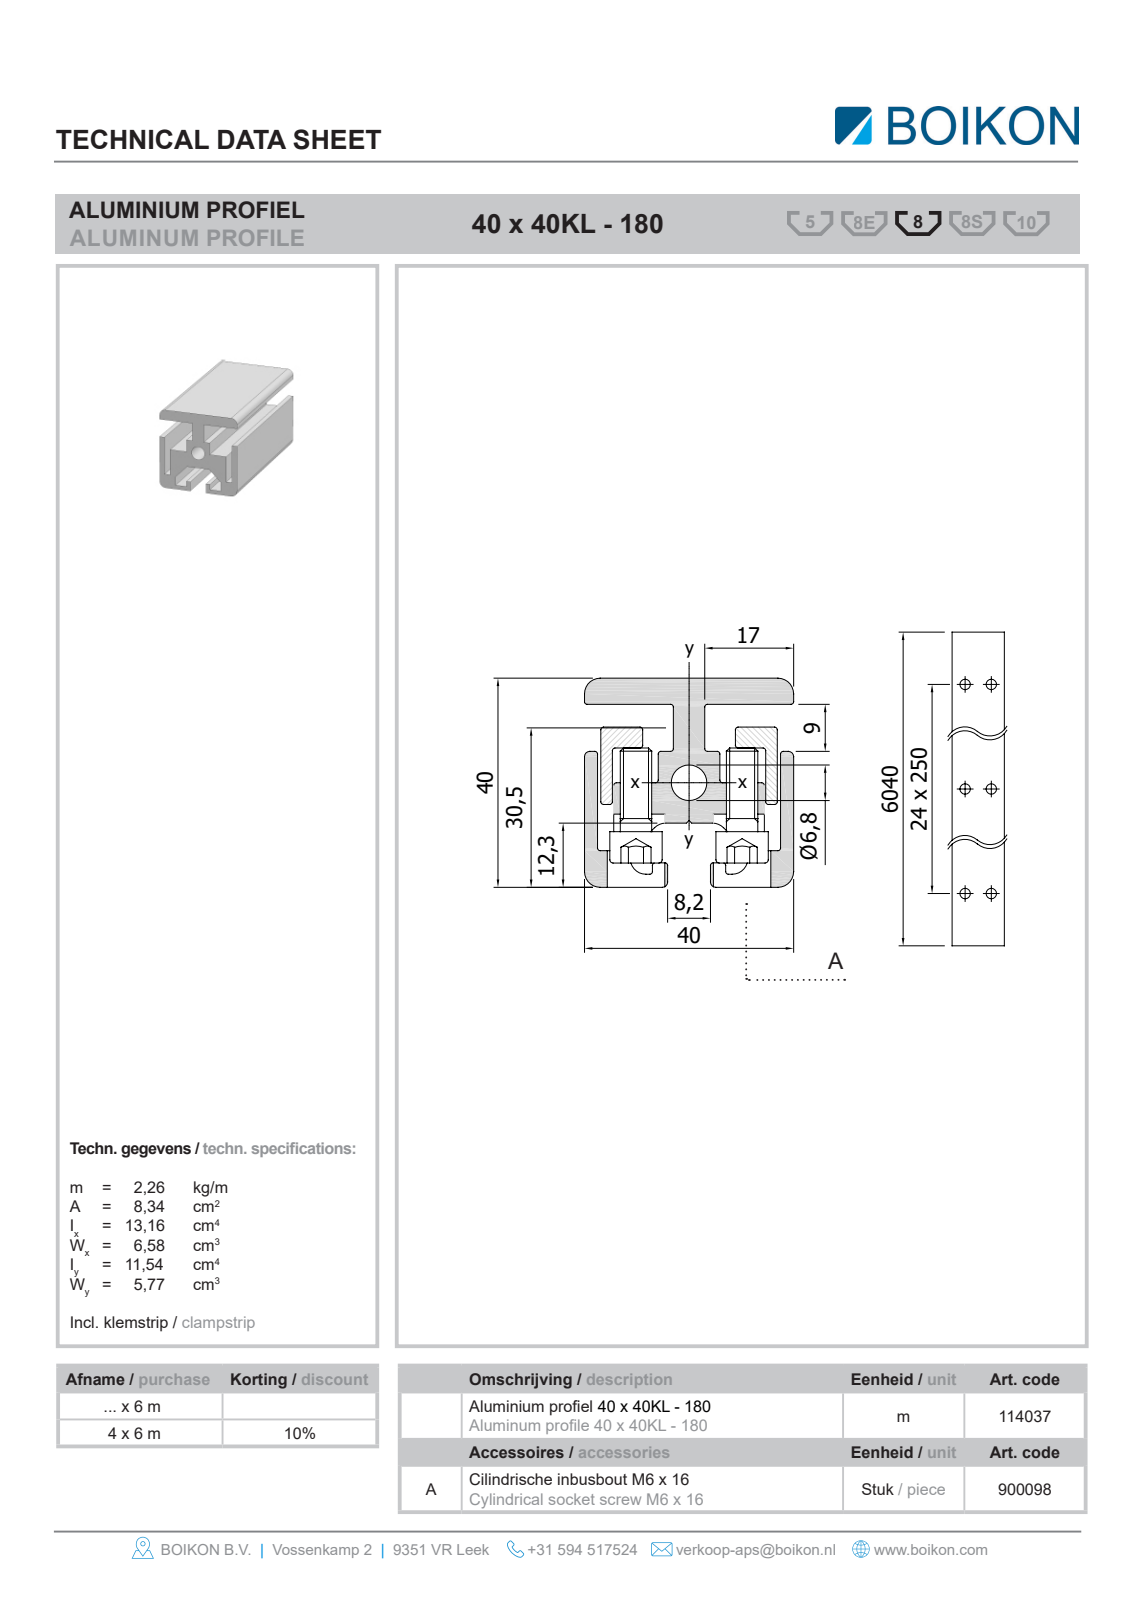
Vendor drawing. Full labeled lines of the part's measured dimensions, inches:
Part name (STEP PRODUCT): Root; 11403740x40-KL180BOIKON0
STEP written by: HiCAD 2013 1802.4 Build 509 (AUTOMOTIVE_DESIGN)
Units: inches
Bodies: 1 solid, 45 faces (40 planar, 5 cylindrical, 0 other)
Overall size (bounding box): 39.37 × 1.575 × 1.575
Volume: 50.04 in³ · Surface area: 590.6 in²
Round holes (diameter × count): ⌀0.268 ×1
Partial cylindrical surfaces — rounded edges, fillets, slot ends (radius × count): R0.118 ×4
Main face-to-face distances: 1.575, 1.378, 0.197, 0.118, 0.098, 1.476, 0.787, 0.807, 0.453, 0.217
